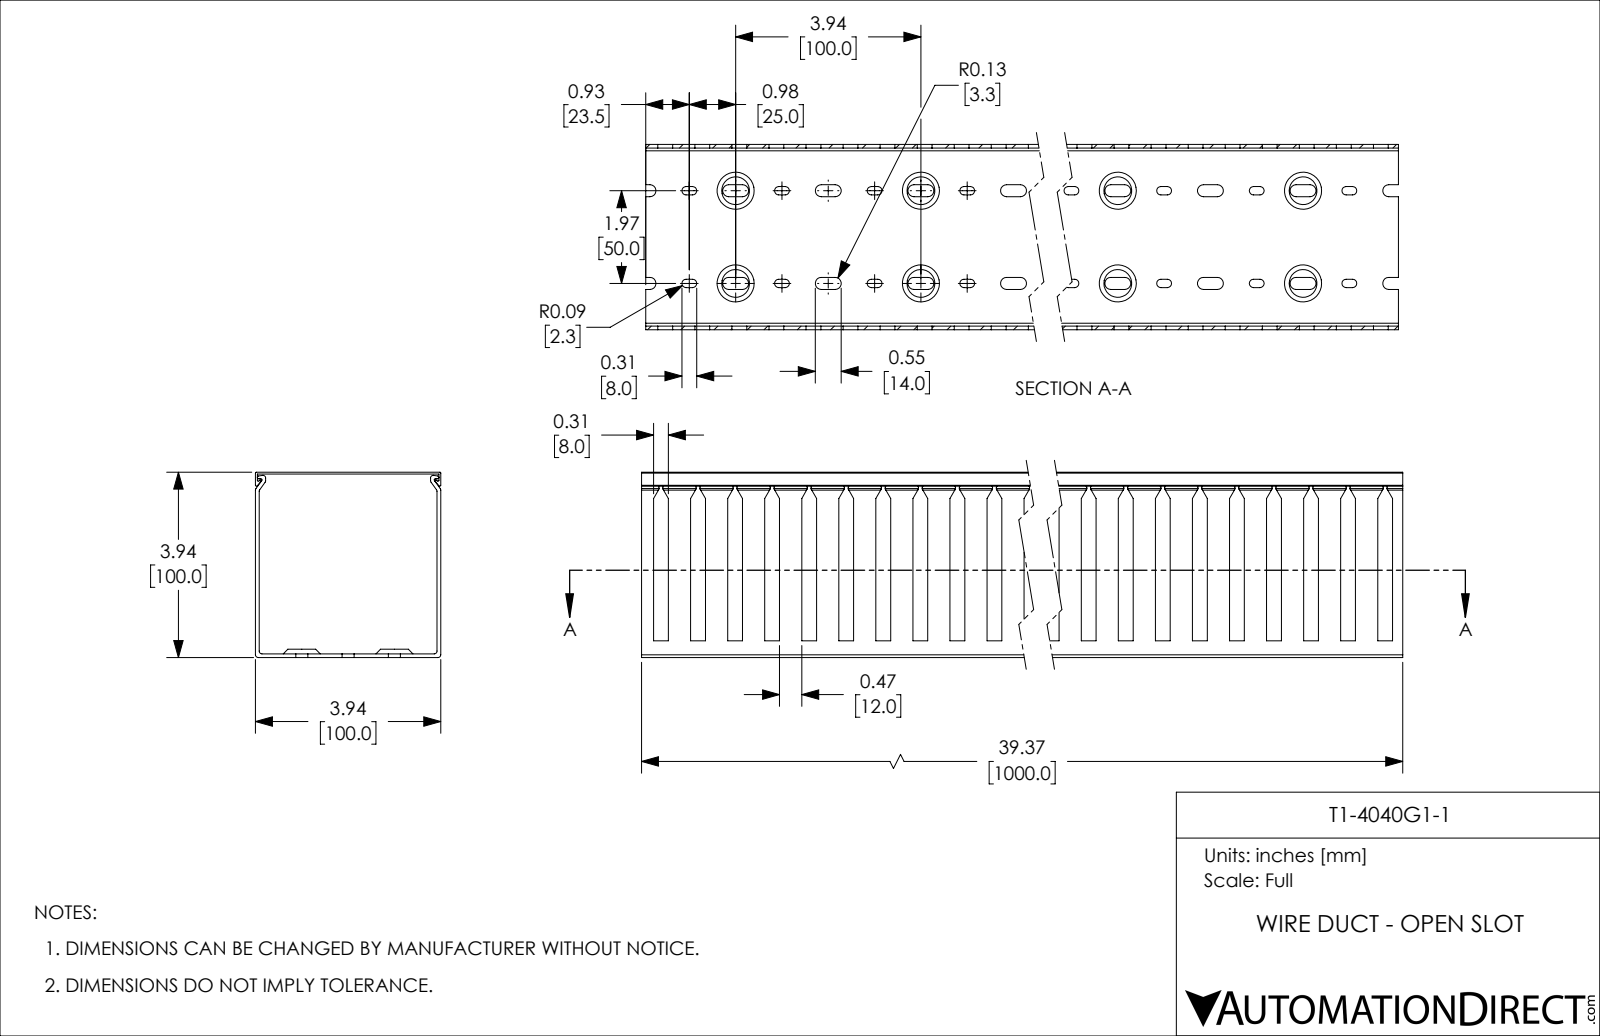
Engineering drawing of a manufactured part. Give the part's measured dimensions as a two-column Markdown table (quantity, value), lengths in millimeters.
| quantity | value |
| --- | --- |
| part name | T1-4040G1-1 |
| STEP written by | SolidWorks 2021 (CONFIG_CONTROL_DESIGN) |
| units | millimeters |
| bodies | 2 solids, 1063 faces (562 planar, 461 cylindrical, 40 other) |
| overall size | 1000 × 100 × 100 |
| volume | 684 884 mm³ |
| surface area | 810 074 mm² |
| partial cylindrical surfaces (radius × count) | 3.25 × 100, 2.25 × 80, 1.5 × 12, 0.5 × 8, 0.75 × 6 |
| main face-to-face distances | 2, 98, 100, 1, 99, 97, 96, 4.5, 20, 94.5 |
